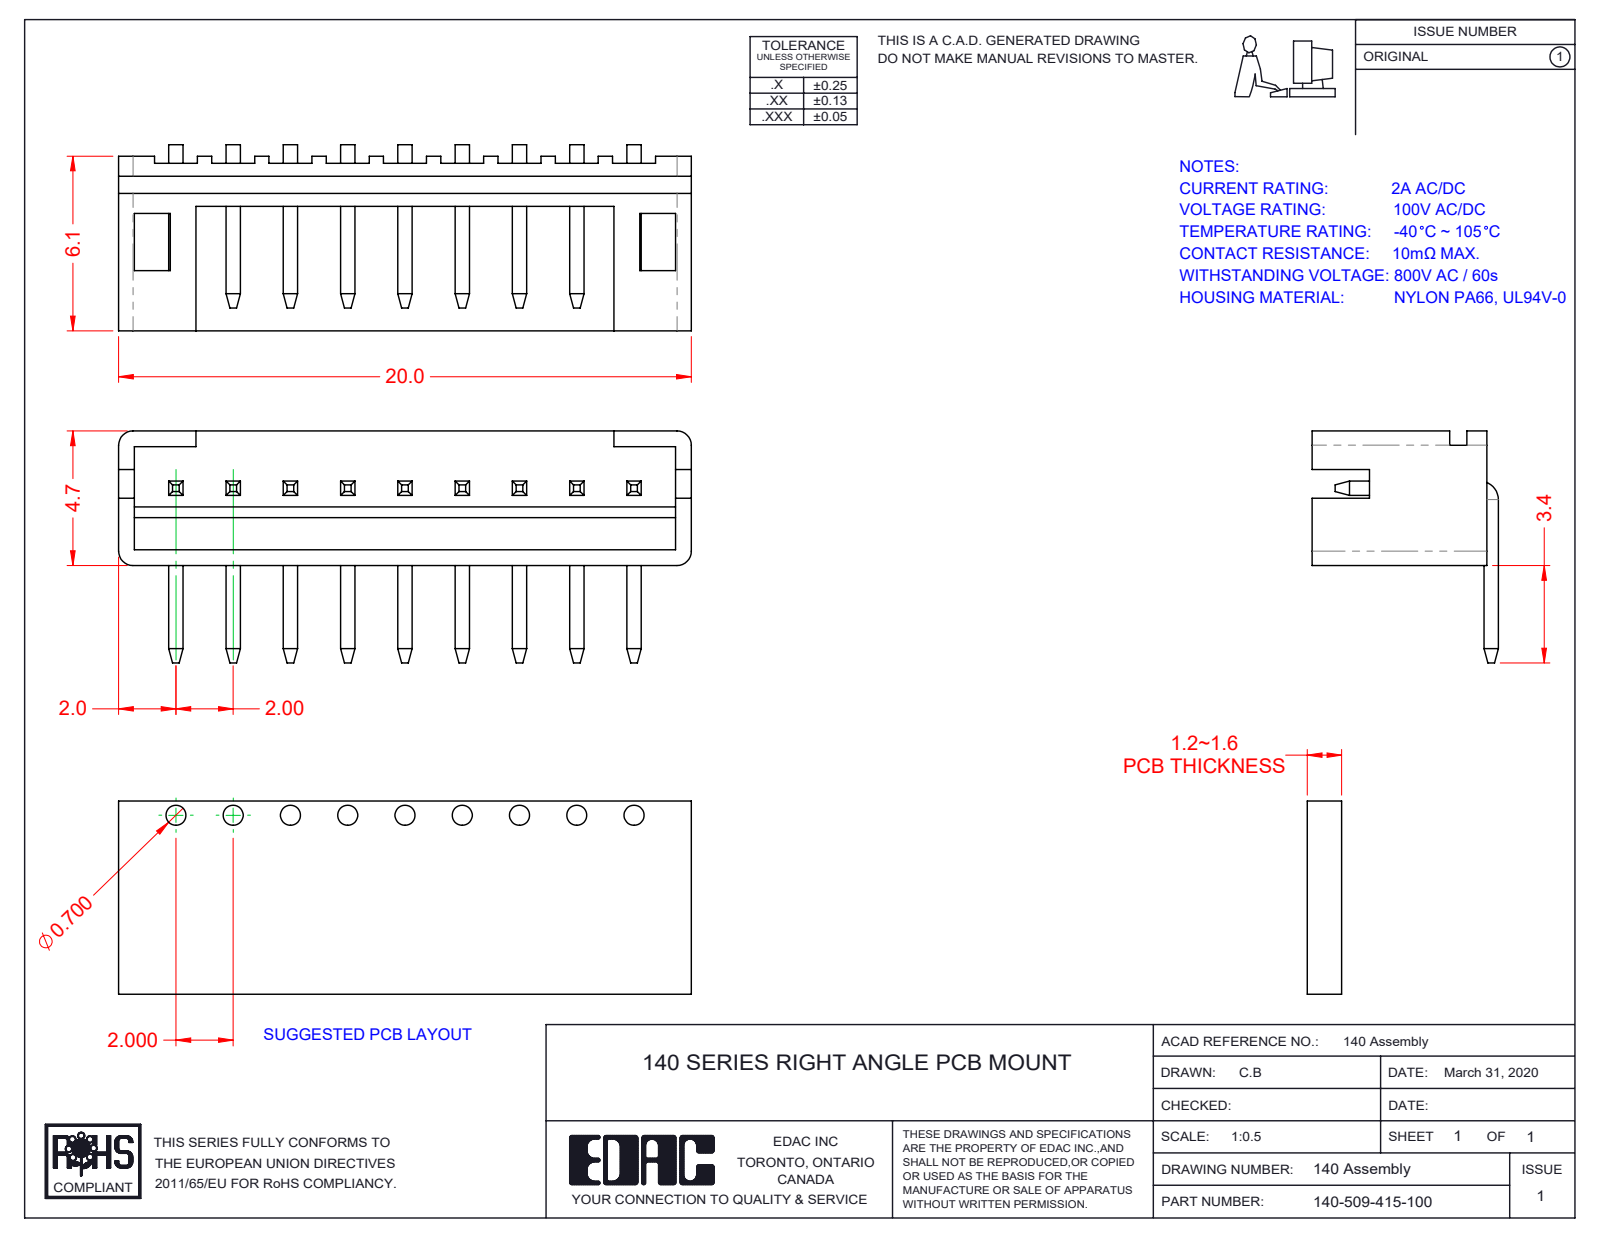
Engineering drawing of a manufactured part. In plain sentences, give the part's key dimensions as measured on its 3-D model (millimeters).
The part is named "RA LI Housing_509; 140-509-415-100; RA LI Contact_Str". Its 3-D file was written by "SolidWorks 2020 (CONFIG_CONTROL_DESIGN)". It is 10 solids with 310 faces: 286 planar, 24 cylindrical and 0 other. Overall it measures 20 by 8.1 by 6.5 millimeters. Its volume is 220 cubic millimeters and its surface area 830 square millimeters. Partial cylindrical surfaces (rounded edges, fillets, slot ends): 4 of radius 0.5, 1 of radius 0.15, 1 of radius 0.65. The main face-to-face distances are 0.55, 0.5, 1.5, 1.75, 6, 2, 4, 8, 4.15, 6.5.
